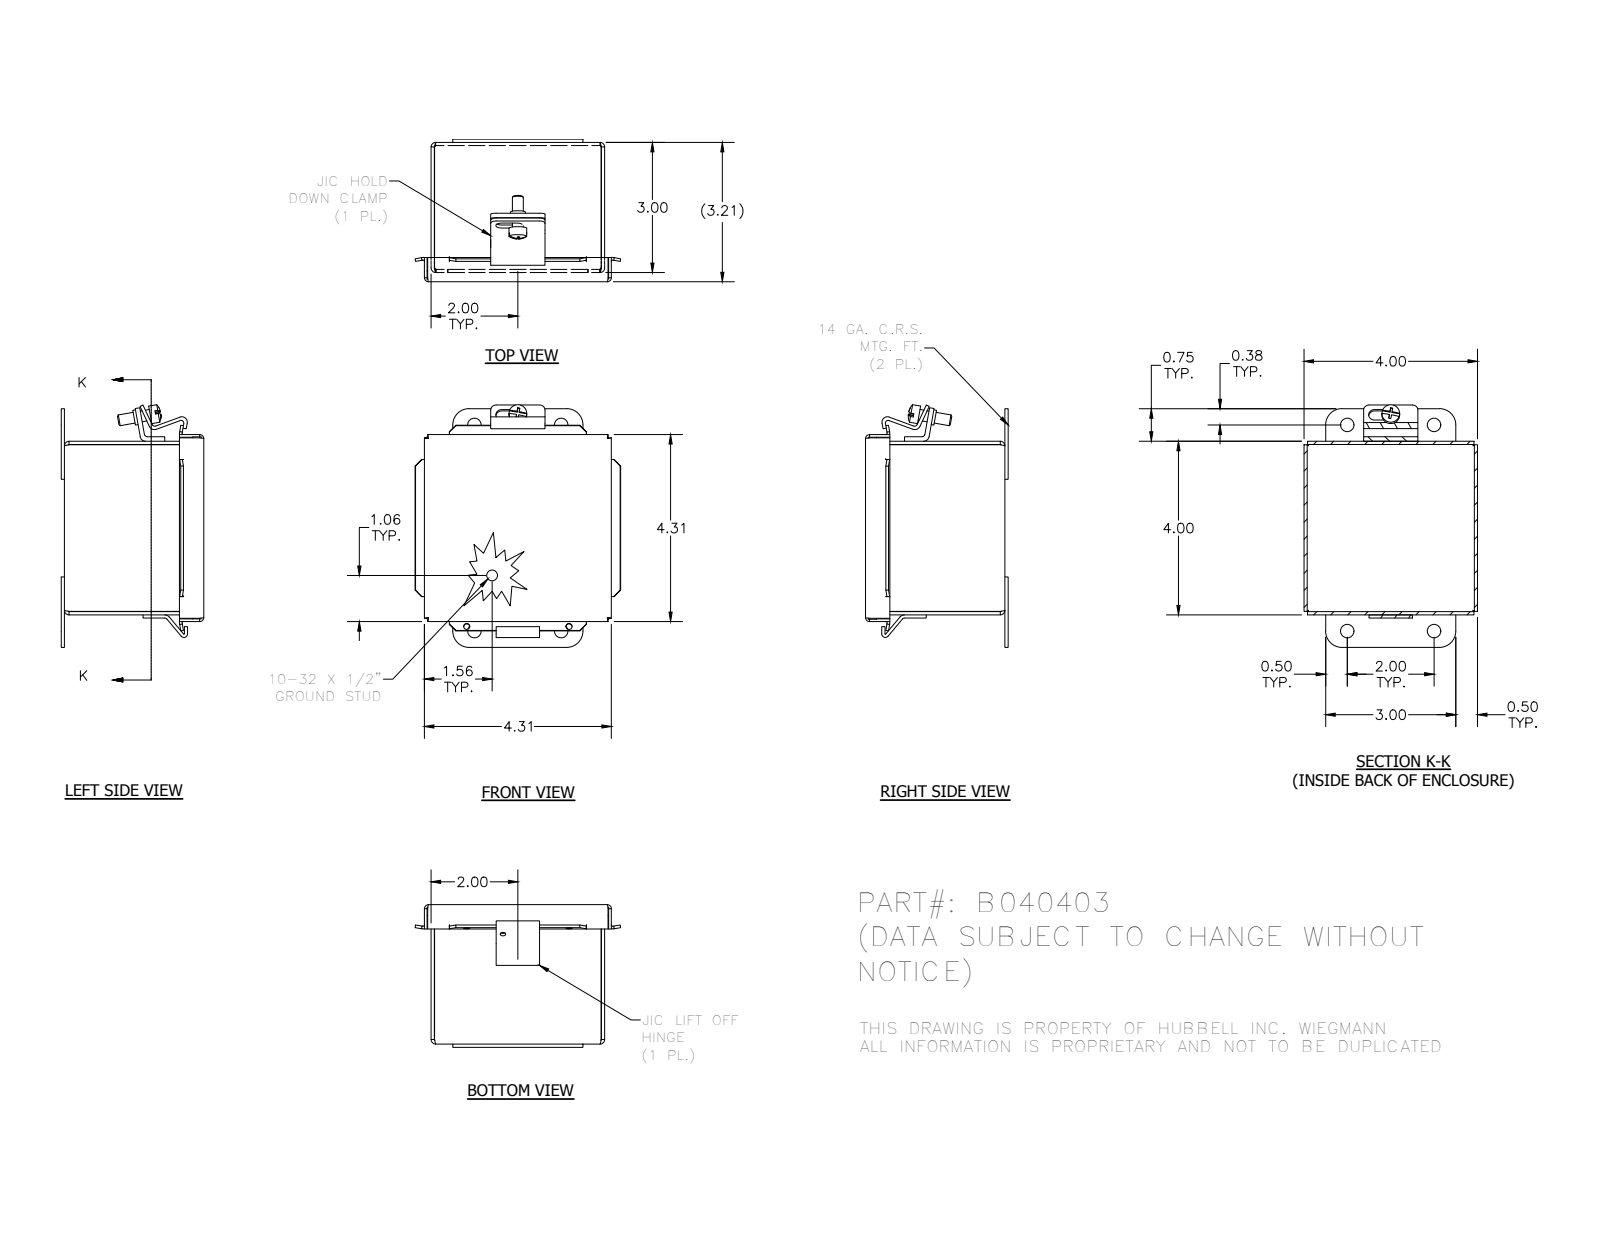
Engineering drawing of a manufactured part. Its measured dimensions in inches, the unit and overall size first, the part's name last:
Units: inches
Overall size (bounding box): 5.593 × 4.739 × 3.287
Round holes (diameter × count): ⌀0.31 ×4, ⌀0.14 ×2, ⌀0.125 ×1, ⌀0.196 ×1
Round bosses / shafts (diameter × count): ⌀0.25 ×2, ⌀0.41 ×1, ⌀0.344 ×1, ⌀0.19 ×1
Partial cylindrical surfaces — rounded edges, fillets, slot ends (radius × count): R0.031 ×16, R0.093 ×8, R0.105 ×8, R0.125 ×4, R0.375 ×4, R0.063 ×3, R0.126 ×3, R0.133 ×2
Main face-to-face distances: 0.074, 3.926, 3.15, 4, 3.852, 3.212, 0.062, 3.076, 3.138, 0.075
Hole centre spacings: 2, 4.75, 5.071, 5.154, 2.357
Volume: 9.375 in³ · Surface area: 246.9 in²
Bodies: 11 solids, 310 faces (215 planar, 65 cylindrical, 30 other)
Part name (STEP PRODUCT): B040403; 3481; C1001; H4050550 (+6 more)
STEP written by: Autodesk Inventor 2012 (AUTOMOTIVE_DESIGN)
